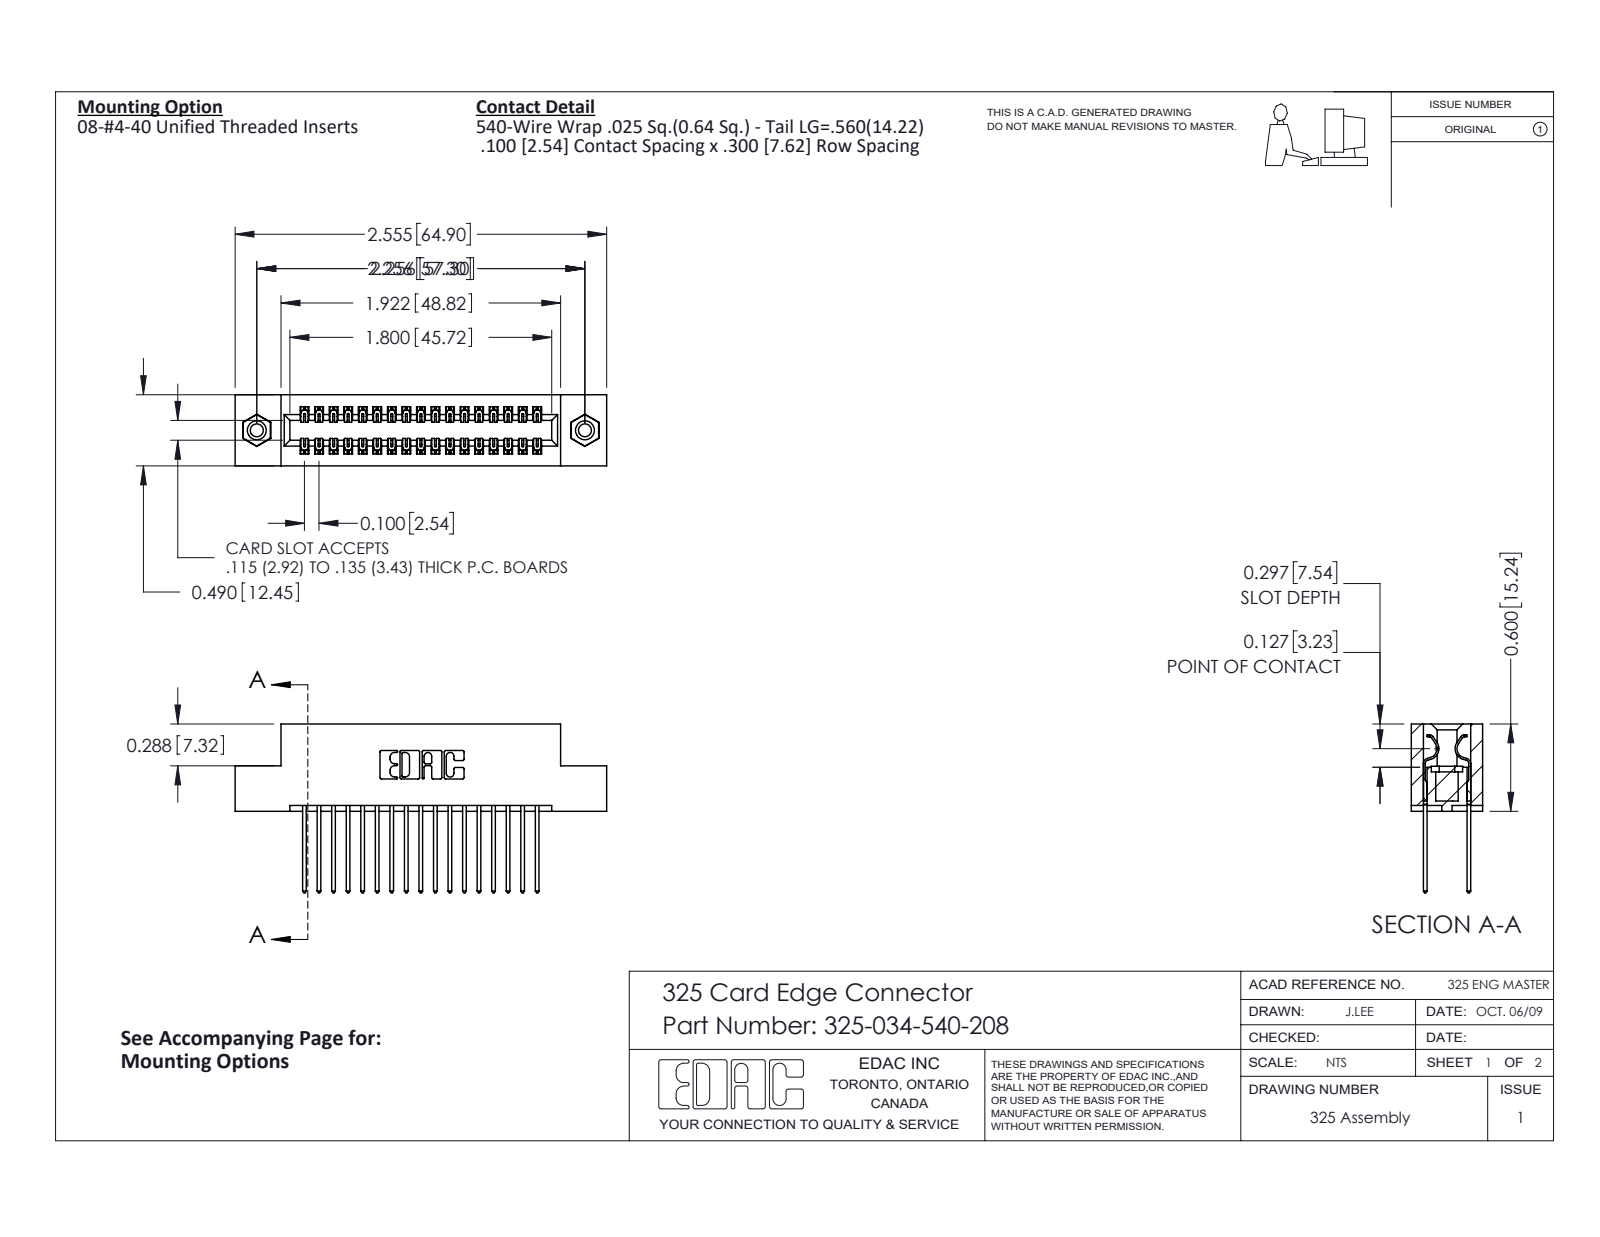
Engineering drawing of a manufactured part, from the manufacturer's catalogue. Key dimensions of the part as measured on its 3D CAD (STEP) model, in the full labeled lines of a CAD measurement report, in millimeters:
Part name (STEP PRODUCT): 325-292-001_325-293-140; 325 Part_TI; 325-034-540-208; 345-250-001_345-250-003-102
STEP written by: SolidWorks 2016 (CONFIG_CONTROL_DESIGN)
Units: millimetres
Bodies: 37 solids, 1942 faces (1326 planar, 600 cylindrical, 16 other)
Overall size (bounding box): 64.9 × 29.5 × 12.4
Volume: 8 280 mm³ · Surface area: 10 050 mm²
Round holes (diameter × count): ⌀2.3 ×2, ⌀3.2 ×2, ⌀4.1 ×2
Round bosses / shafts (diameter × count): ⌀3.9 ×2
Partial cylindrical surfaces — rounded edges, fillets, slot ends (radius × count): R0.2 ×51, R0.3 ×34, R0.3 ×22, R0.2 ×6, R0.8 ×6, R0.7 ×3, R0.4 ×2, R0.6 ×2
Main face-to-face distances: 2.1, 10.3, 7.6, 2.7, 9.7, 0.6, 12.4, 8.3, 15.2, 1
Hole centre spacings: 57.3
